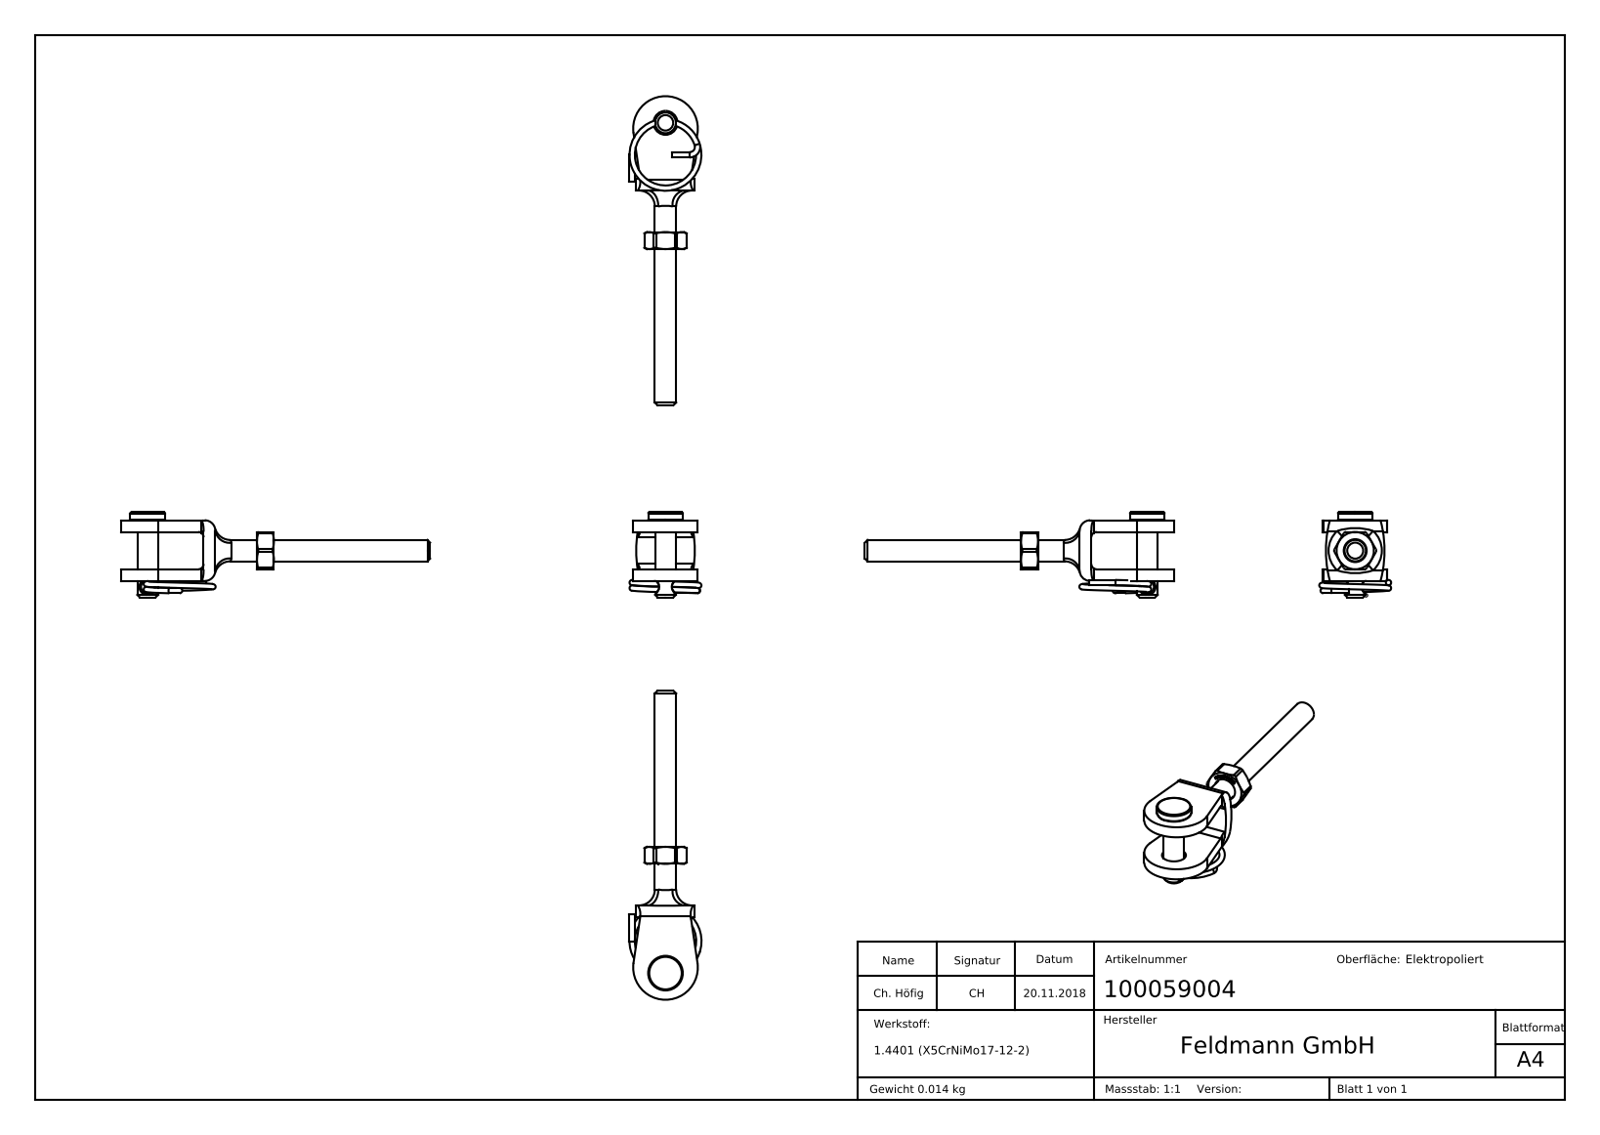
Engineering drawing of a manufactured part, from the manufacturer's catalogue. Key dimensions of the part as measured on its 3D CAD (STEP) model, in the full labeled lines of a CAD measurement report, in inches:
Part name (STEP PRODUCT): 10005900X Teil2; 10005900X Teil1; DIN 934 M4-M20_58321-240-4-L; 10005900X Teil3 (+5 more)
STEP written by: SolidWorks 2018 (CONFIG_CONTROL_DESIGN)
Units: inches
Bodies: 4 solids, 297 faces (134 planar, 27 cylindrical, 136 other)
Overall size (bounding box): 2.283 × 0.63 × 0.531
Volume: 0.109 in³ · Surface area: 3.453 in²
Round holes (diameter × count): ⌀0.098 ×1, ⌀0.13 ×1, ⌀0.177 ×1
Round bosses / shafts (diameter × count): ⌀0.039 ×2, ⌀0.256 ×1, ⌀0.157 ×1, ⌀0.154 ×1
Partial cylindrical surfaces — rounded edges, fillets, slot ends (radius × count): R0.02 ×6, R0.016 ×2, R0.039 ×2, R0.079 ×2, R0.868 ×2, R0.239 ×1
Main face-to-face distances: 0.087, 0.362, 0.276, 0.449, 0.059, 0.508, 0.421, 0.146, 0.394, 0.126
